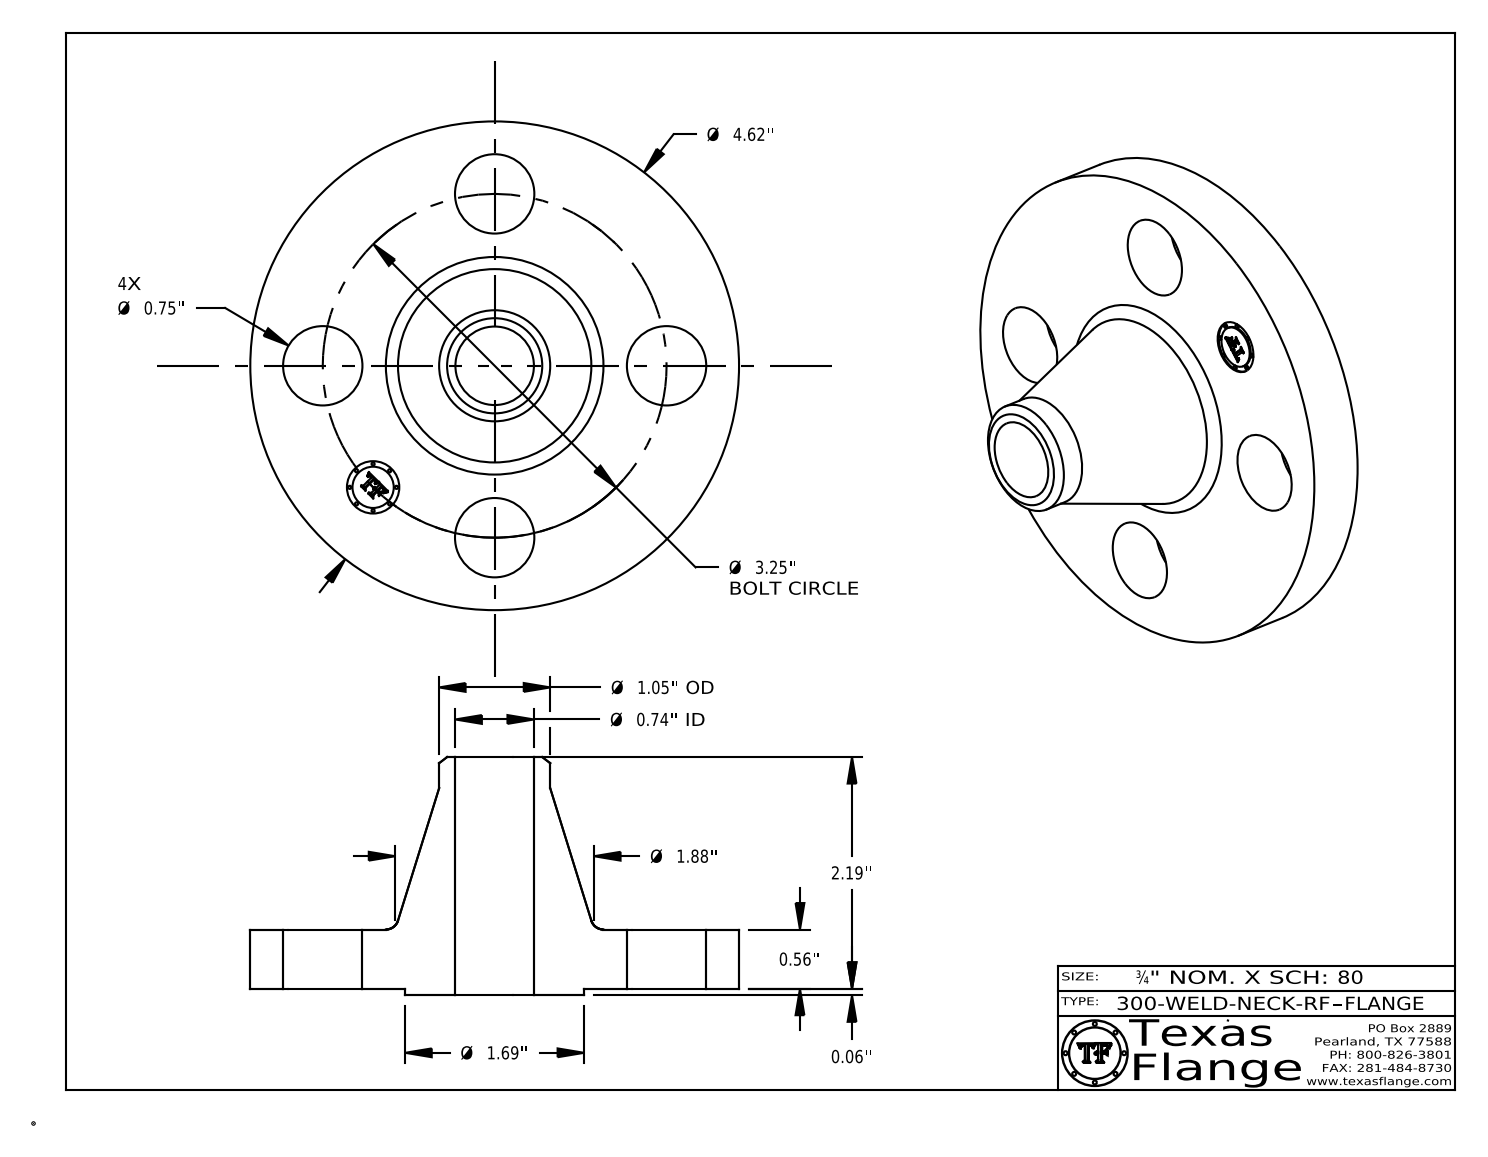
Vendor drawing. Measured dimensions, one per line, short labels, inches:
name: 300-WELD-NECK-RF
written by: CATIA V5 STEP AP214 (AUTOMOTIVE_DESIGN)
unit: in
bodies: 1 solid, 411 faces (369 planar, 36 cylindrical, 6 other)
size: 4.62 × 4.62 × 2.253
volume: 10.13 in³; area: 53.44 in²
holes: 4× ⌀0.75, 1× ⌀0.495, 1× ⌀0.742
bosses: 8× ⌀0.03, 1× ⌀4.62, 1× ⌀1.69, 1× ⌀1.05, 1× ⌀0.39
face distances: 0.56, 0.063, 0.622, 2.253, 2.19, 1.63, 0.607, 0.545, 0.015, 1.645
hole spacings: 1.625, 2.298, 1.244, 3.003, 3.25
